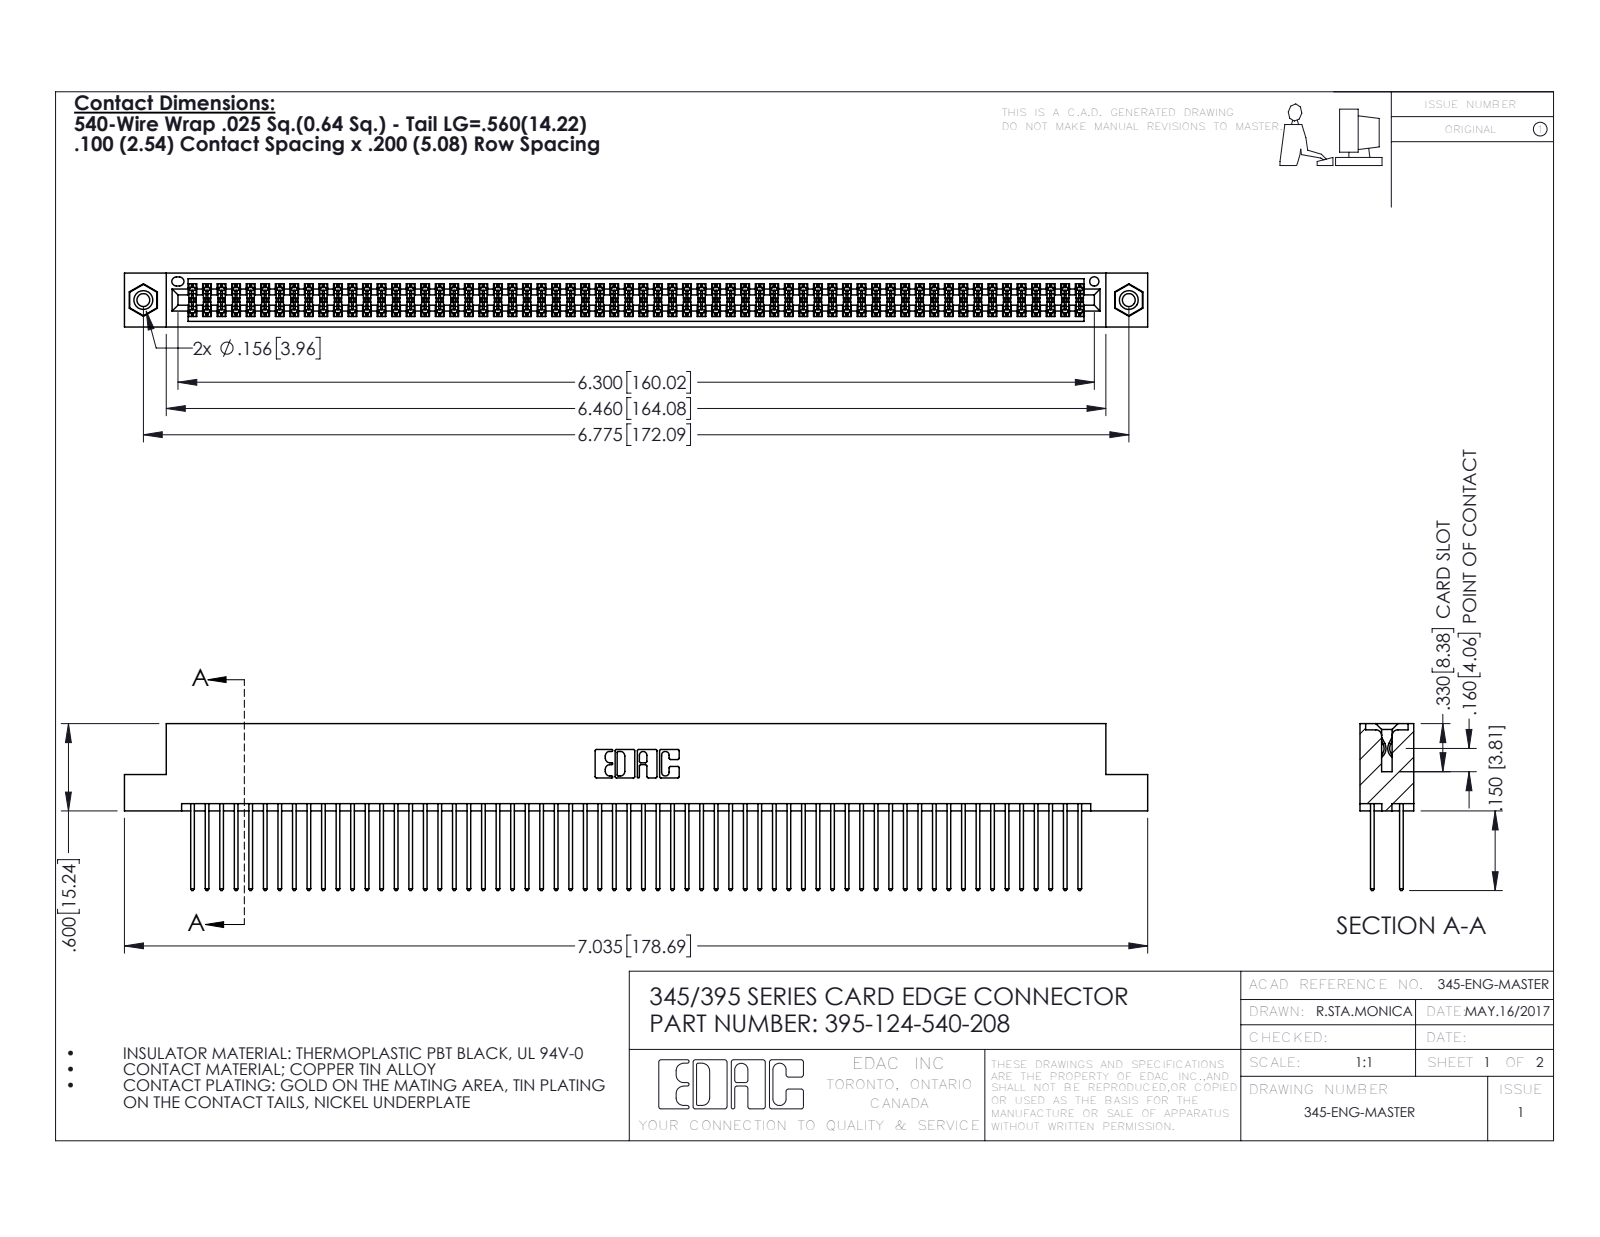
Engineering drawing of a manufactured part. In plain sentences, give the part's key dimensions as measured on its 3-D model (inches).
The part is named "345-292-001_345-293-140; 345 Part_Flush Mounting Lugs - 0.156 Dia-TI; 345-250-001_345-250-003-102; 395-124-540-208". Its 3-D file was written by "SolidWorks 2016 (CONFIG_CONTROL_DESIGN)". It is 127 solids with 6386 faces: 4204 planar, 2166 cylindrical and 16 other. Overall it measures 7.035 by 1.147 by 0.37 inches. Its volume is 1.099 cubic inches and its surface area 45.26 square inches. Round holes: 2 of diameter 0.089, 2 of diameter 0.125, 2 of diameter 0.156, 1 of diameter 0.064. Round bosses or shafts: 2 of diameter 0.155. Partial cylindrical surfaces (rounded edges, fillets, slot ends): 186 of radius 0.006, 124 of radius 0.01, 22 of radius 0.01, 6 of radius 0.007, 6 of radius 0.031, 3 of radius 0.026, 2 of radius 0.014, 2 of radius 0.019. The main face-to-face distances are 0.072, 0.298, 0.2, 0.098, 0.272, 0.025, 0.37, 0.225, 0.175, 0.149. The hole center spacings are 0.27, 6.539, 6.775.
